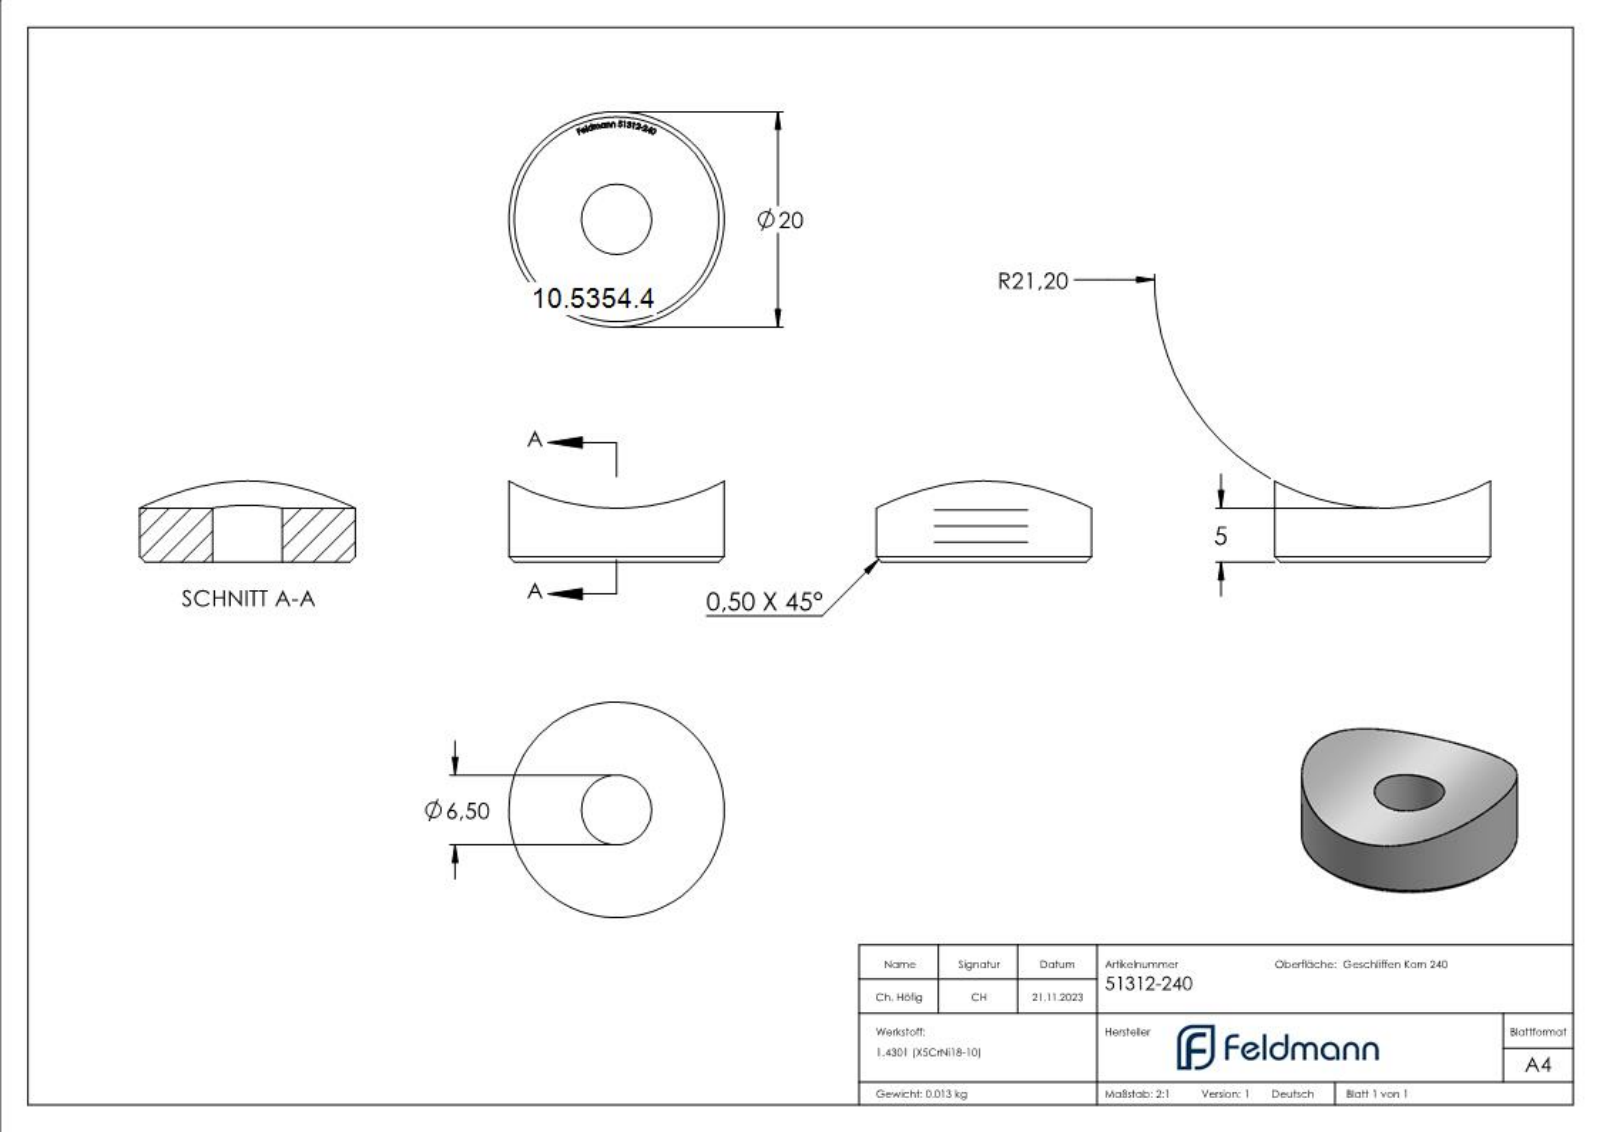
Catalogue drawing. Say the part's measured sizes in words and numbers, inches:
The part is named "51312-240". Its 3-D file was written by "SolidWorks 2018 (CONFIG_CONTROL_DESIGN)". It is 1 solid with 222 faces: 127 planar, 3 cylindrical and 92 other. Overall it measures 0.787 by 0.787 by 0.296 inches. Its volume is 0.097 cubic inches and its surface area 1.632 square inches. Round holes: 1 of diameter 0.256. Round bosses or shafts: 1 of diameter 0.787. Partial cylindrical surfaces (rounded edges, fillets, slot ends): 1 of radius 0.835. The main face-to-face distances are 0.013, 0.013, 0.015, 0.021, 0.021, 0.014, 0.012, 0.016, 0.015.
